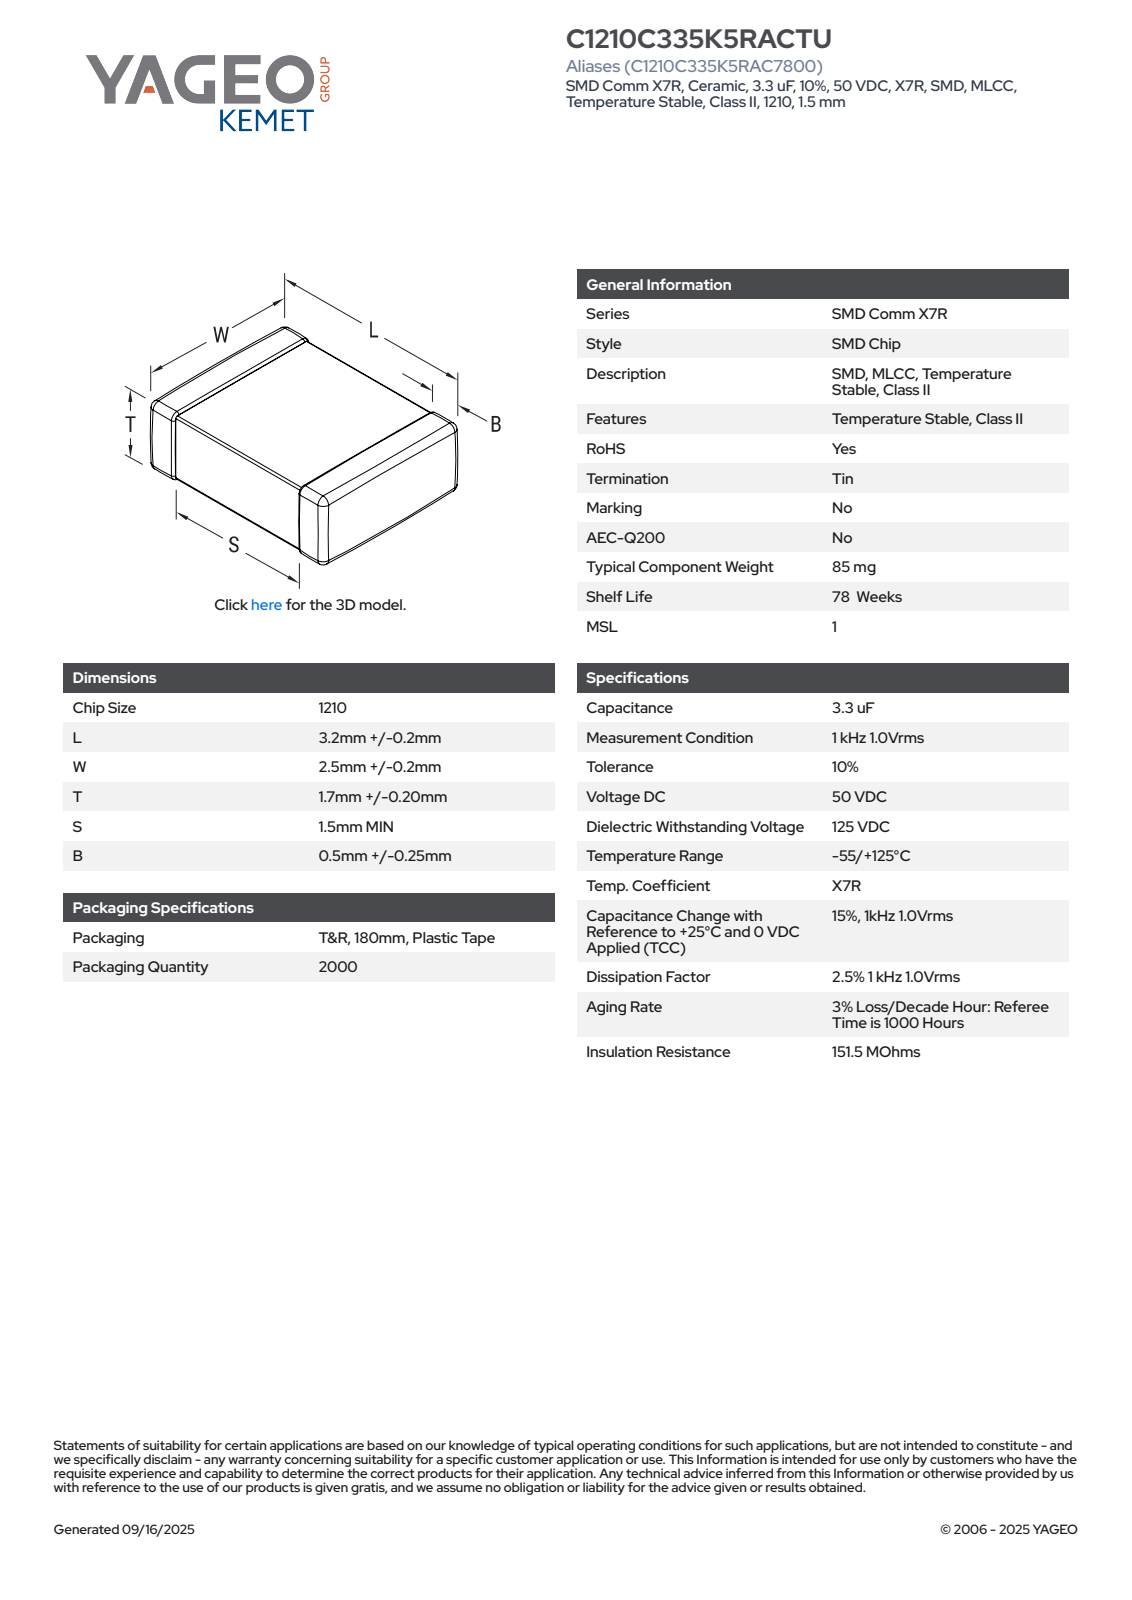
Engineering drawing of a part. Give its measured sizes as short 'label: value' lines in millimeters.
name: CCS_CCSTD_1210_L3.4W2.7T1.9B0.5
written by: SolidWorks 2021 (AUTOMOTIVE_DESIGN)
unit: mm
bodies: 4 solids, 125 faces (71 planar, 38 cylindrical, 16 other)
size: 3.4 × 2.7 × 1.9
volume: 16 mm³; area: 41 mm²
face distances: 1.84, 1.78, 3.4, 2.64, 1.9, 2.58, 2.7, 1.85, 1.79, 0.4
